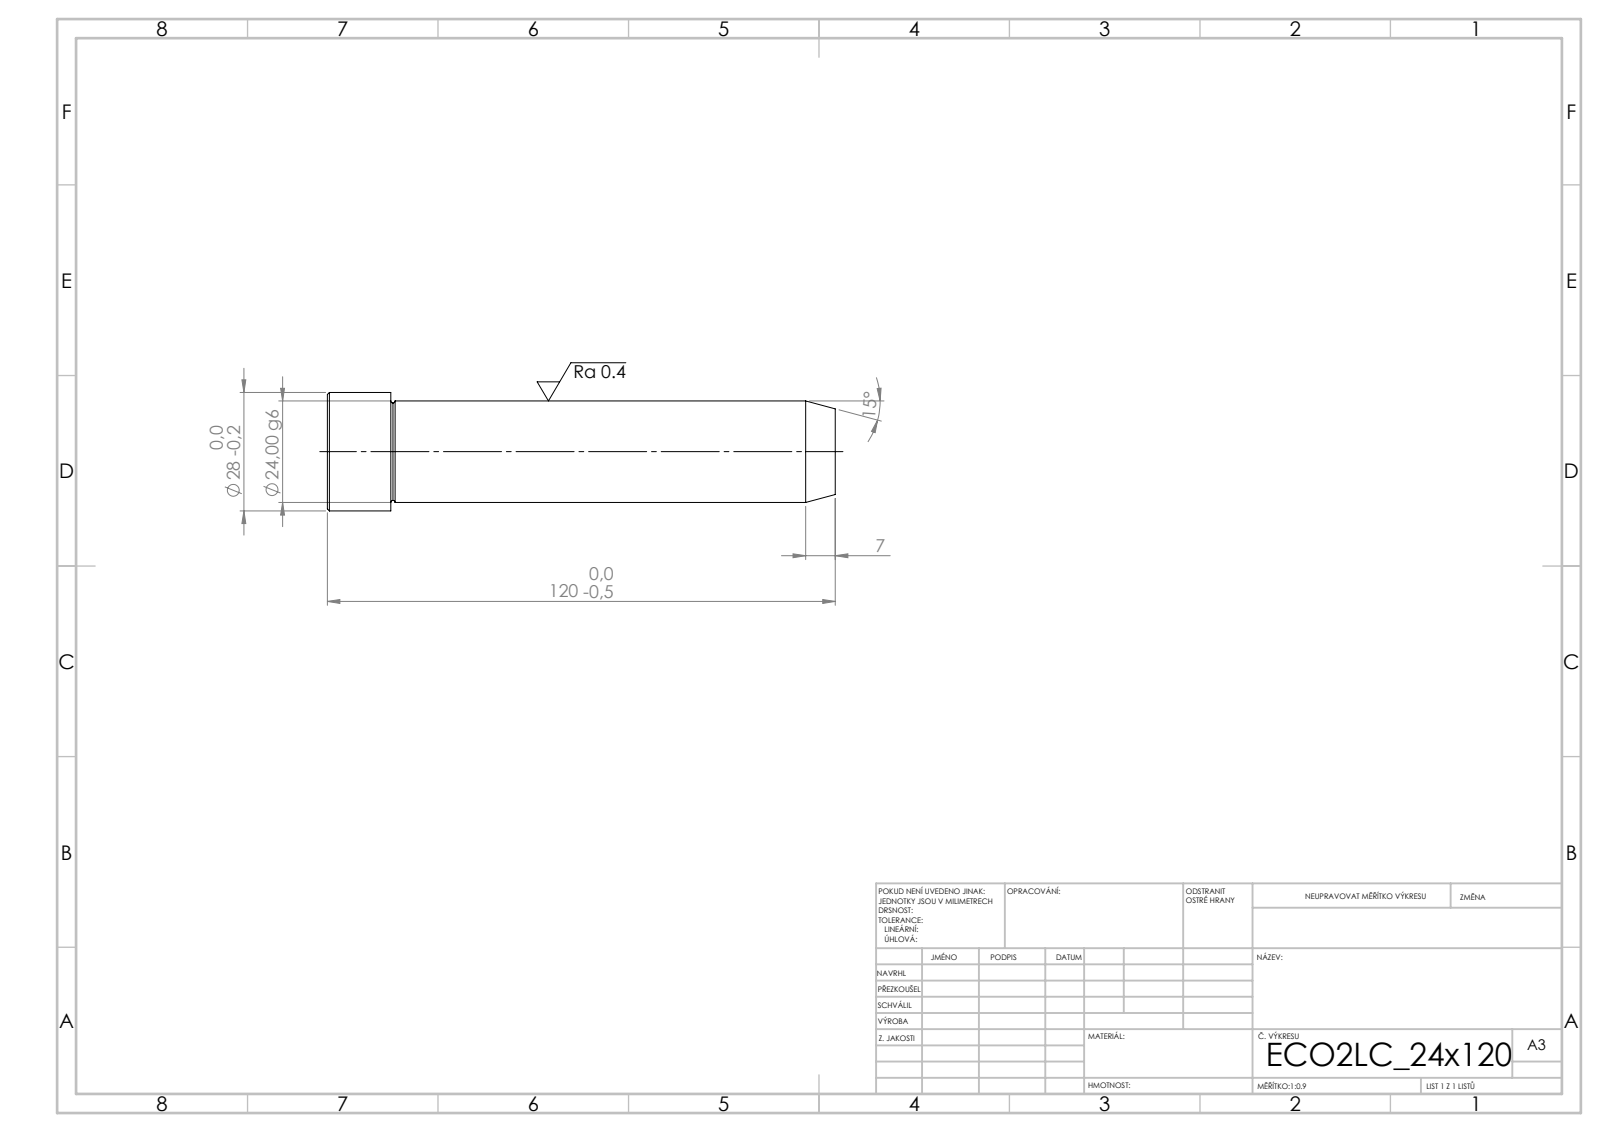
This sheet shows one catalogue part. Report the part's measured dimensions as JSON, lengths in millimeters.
{"step_written_by": "SolidWorks 2019 (CONFIG_CONTROL_DESIGN)", "units": "millimeters", "bodies": {"solids": 1, "faces": 15, "planar": 3, "cylindrical": 4, "other": 8}, "overall_size": [120, 28, 28], "volume_mm3": 56228, "surface_area_mm2": 10327, "round_bosses_or_shafts": [[28, 1], [24, 1]], "face_to_face_distances": [120, 105, 15]}
